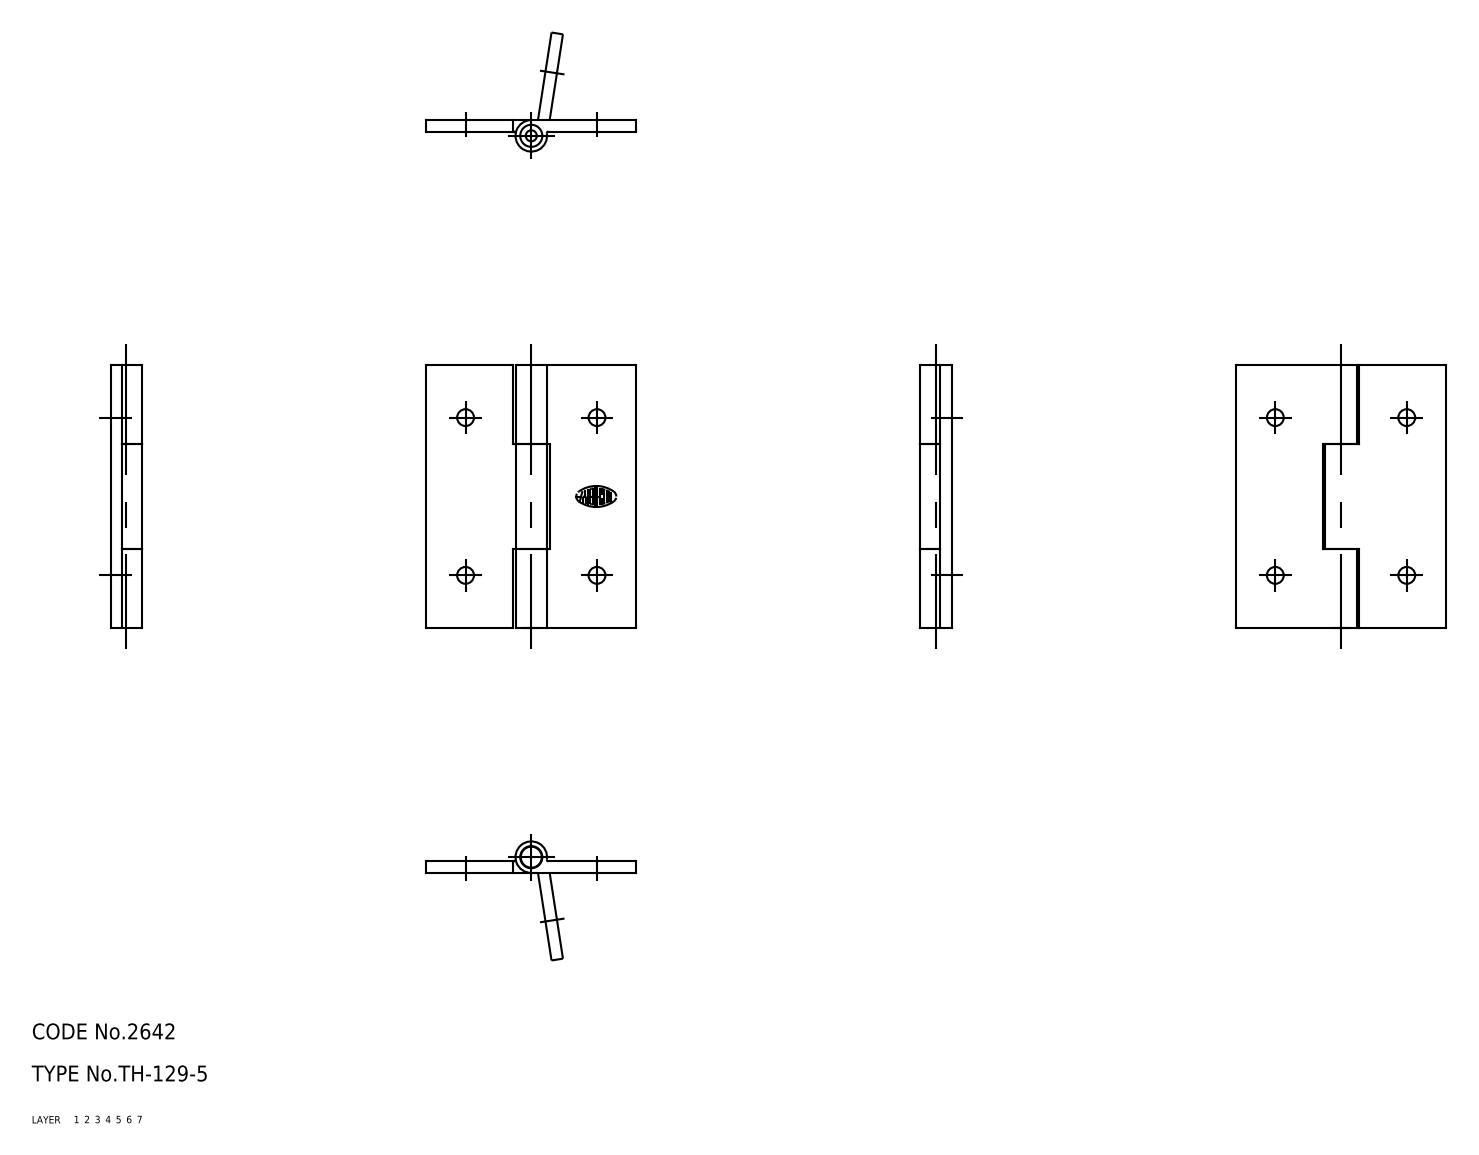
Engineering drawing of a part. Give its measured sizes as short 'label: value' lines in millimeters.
name: shaft; hinge piece_B; hinge piece_A; TH_129_5_3314_36
written by: CADfix (AUTOMOTIVE_DESIGN)
unit: mm
bodies: 3 solids, 44 faces (0 planar, 0 cylindrical, 44 other)
size: 50 × 40 × 6
volume: 5 103 mm³; area: 5 851 mm²
